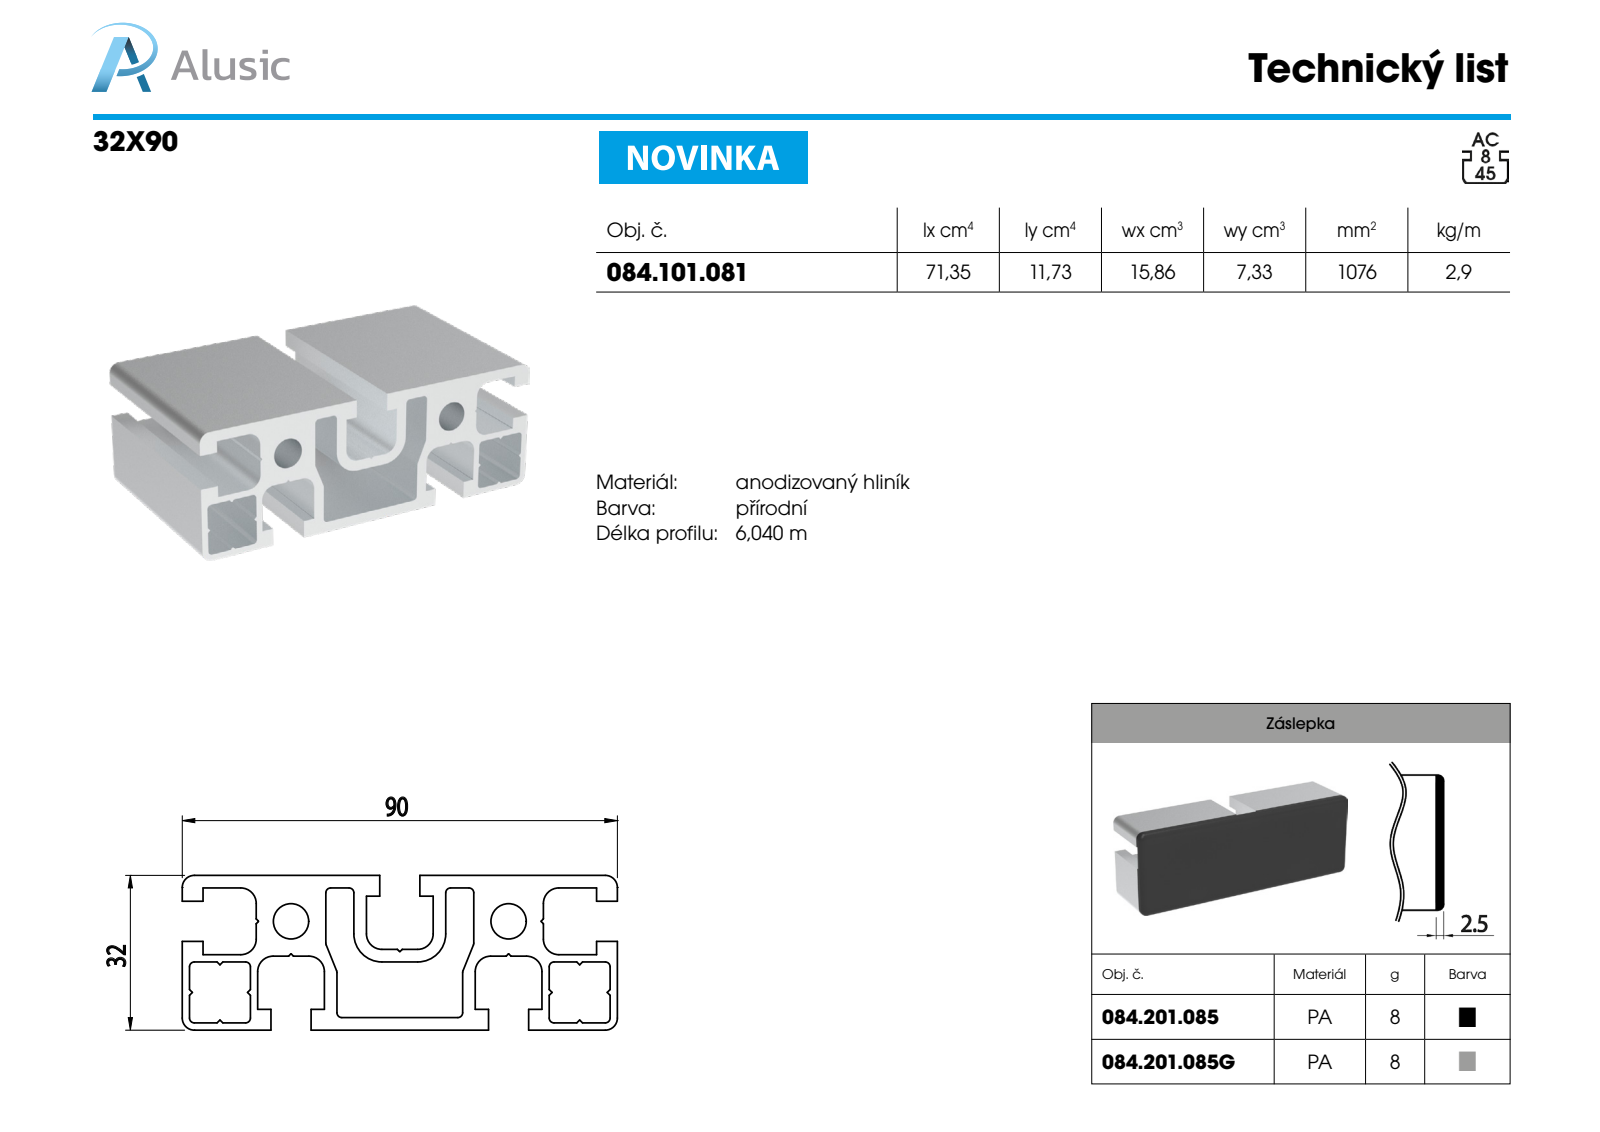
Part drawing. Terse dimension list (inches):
name: 084.101.081
written by: SolidWorks 2018 (AUTOMOTIVE_DESIGN)
unit: in
bodies: 1 solid, 160 faces (105 planar, 55 cylindrical, 0 other)
size: 3.937 × 3.543 × 1.26
volume: 6.564 in³; area: 114.5 in²
holes: 2× ⌀0.287
rounds: 18× R0.039, 15× R0.004, 10× R0.126, 4× R0.098, 2× R0.228
face distances: 0.555, 1.26, 0.102, 0.602, 0.059, 0.543, 1.157, 0.614, 0.886, 0.646
hole spacings: 1.772
